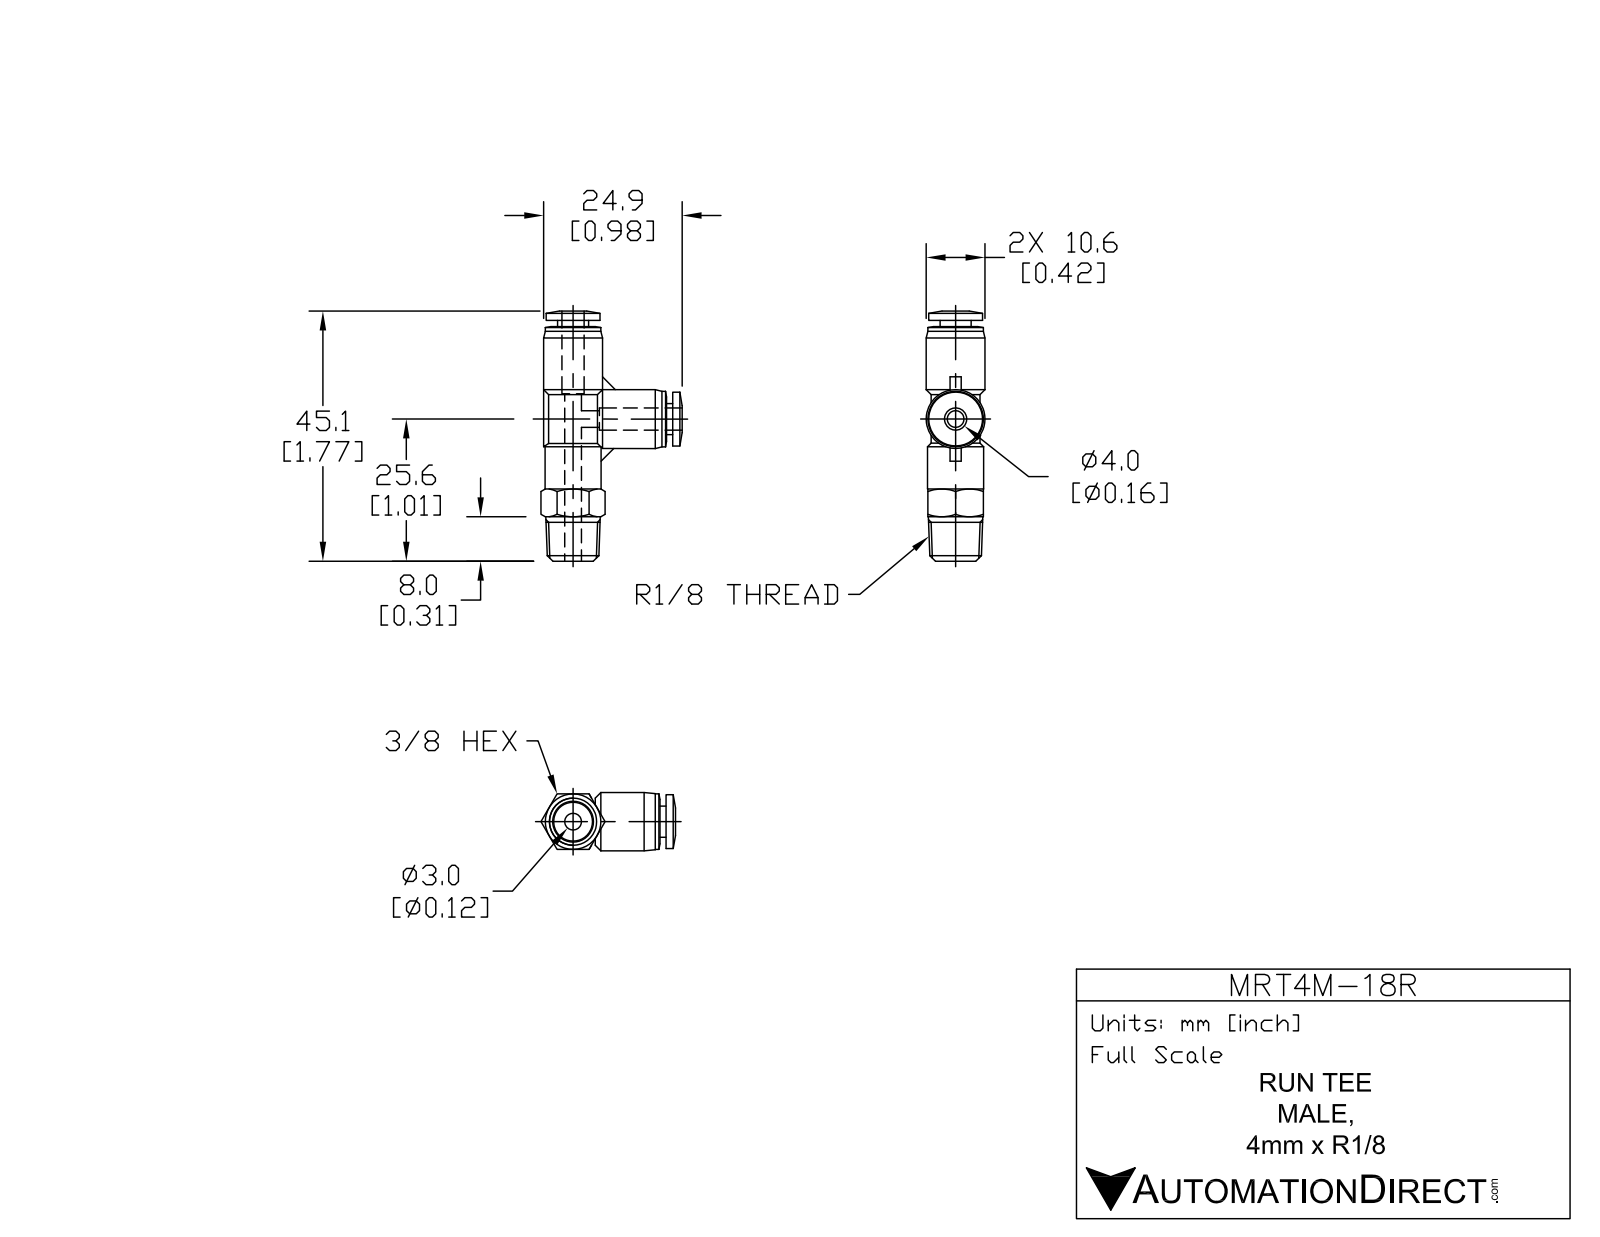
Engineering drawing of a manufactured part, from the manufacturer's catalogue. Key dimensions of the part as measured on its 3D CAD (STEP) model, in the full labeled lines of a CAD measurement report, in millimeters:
Part name (STEP PRODUCT): MRT4M-18R
STEP written by: SolidWorks 2015 (AUTOMOTIVE_DESIGN)
Units: millimetres
Bodies: 1 solid, 102 faces (25 planar, 33 cylindrical, 44 other)
Overall size (bounding box): 45 × 25.2 × 10.6
Volume: 3 970 mm³ · Surface area: 2 952 mm²
Round holes (diameter × count): ⌀3 ×2, ⌀4.3 ×2
Round bosses / shafts (diameter × count): ⌀10.6 ×2, ⌀10 ×2, ⌀9.7 ×2, ⌀8.8 ×2, ⌀5.6 ×2, ⌀10.1 ×1
Main face-to-face distances: 10, 1.1, 43.3, 4, 6, 42.1, 12, 13.1, 2, 30.1
